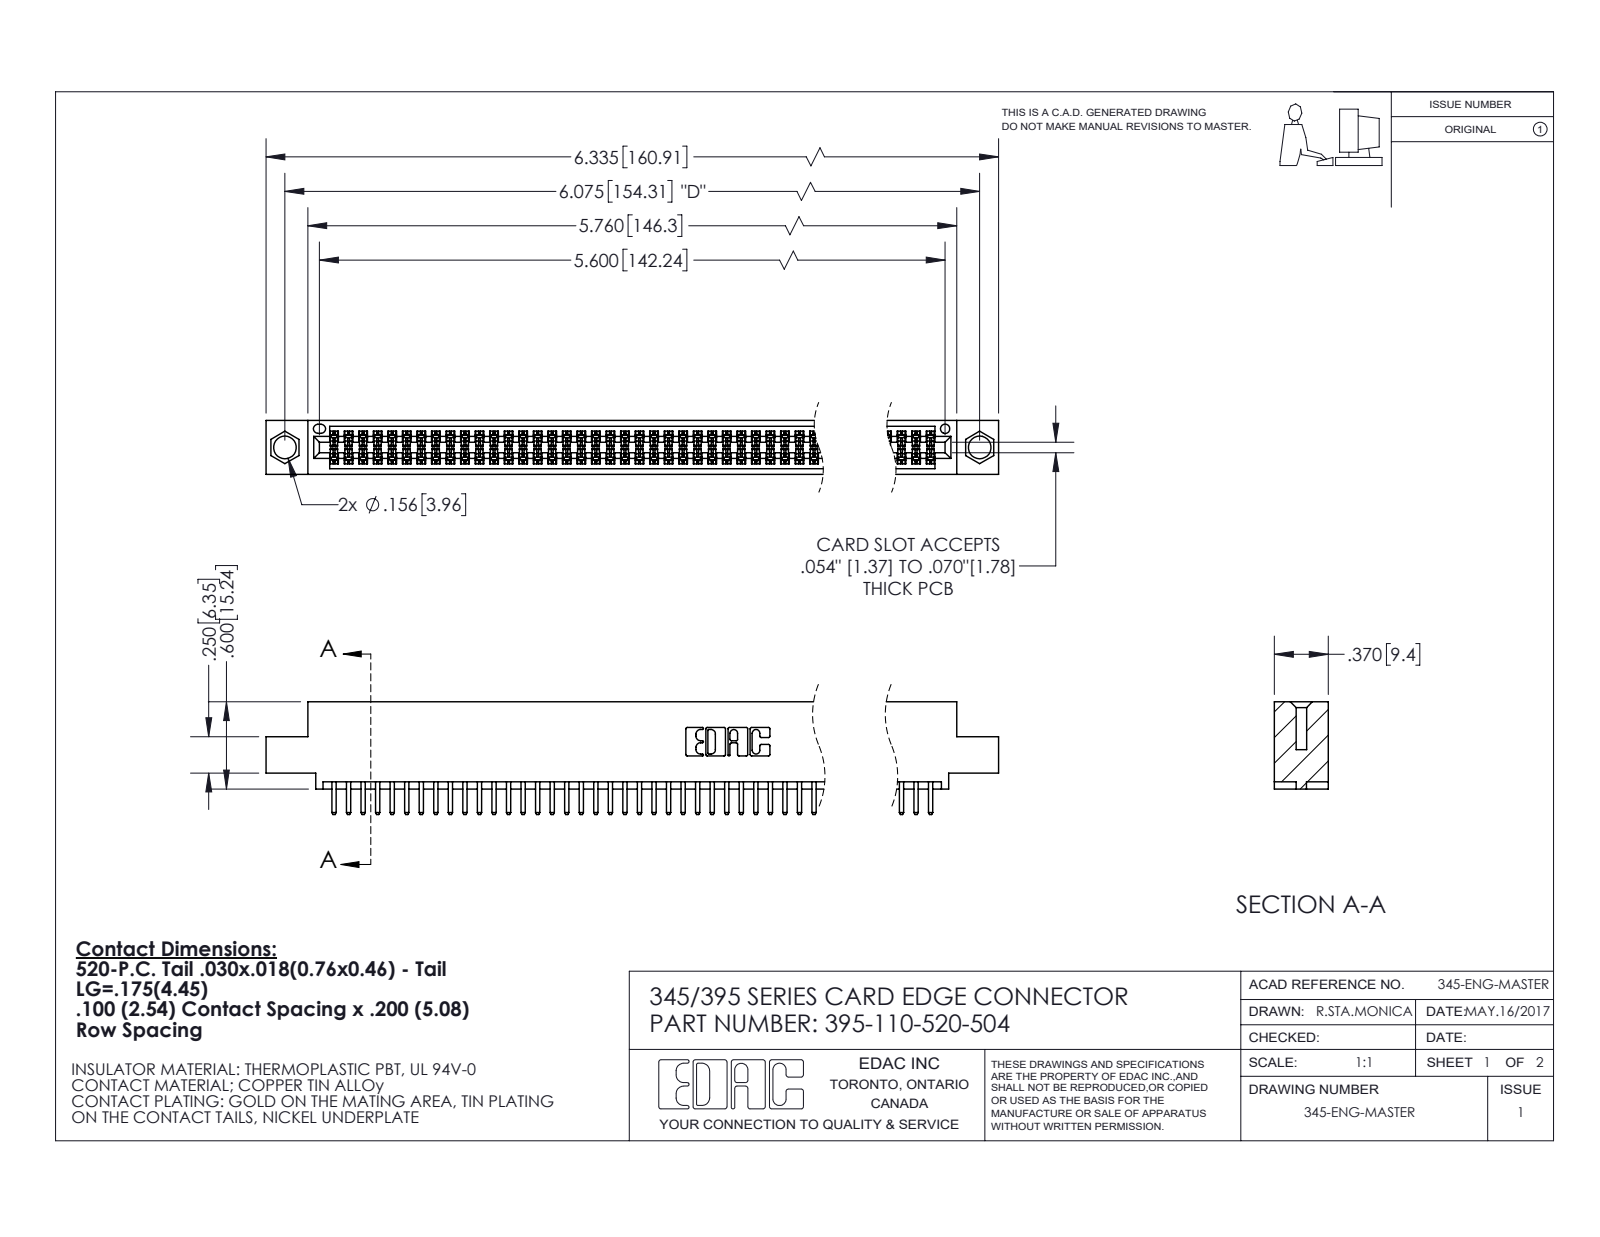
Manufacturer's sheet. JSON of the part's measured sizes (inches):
{"part_name": "345 Part_0.110 Offset - 0.156 Dia-TI; 345-292-001_345-293-120; 395-110-520-504", "step_written_by": "SolidWorks 2020 (CONFIG_CONTROL_DESIGN)", "units": "inches", "bodies": {"solids": 111, "faces": 6084, "planar": 3948, "cylindrical": 2136, "other": 0}, "overall_size": [6.335, 0.775, 0.37], "volume_in3": 0.947, "surface_area_in2": 35.71, "round_holes": [[0.156, 2], [0.064, 1]], "partial_cylinders_radius": [[0.006, 165], [0.01, 114], [0.01, 22], [0.007, 6], [0.031, 6], [0.026, 3], [0.014, 2], [0.019, 2]], "face_to_face_distances": [0.298, 0.072, 0.2, 0.37, 0.098, 0.272, 0.025, 0.225, 0.022, 0.072], "hole_center_spacings": [0.27, 5.839, 6.075]}
